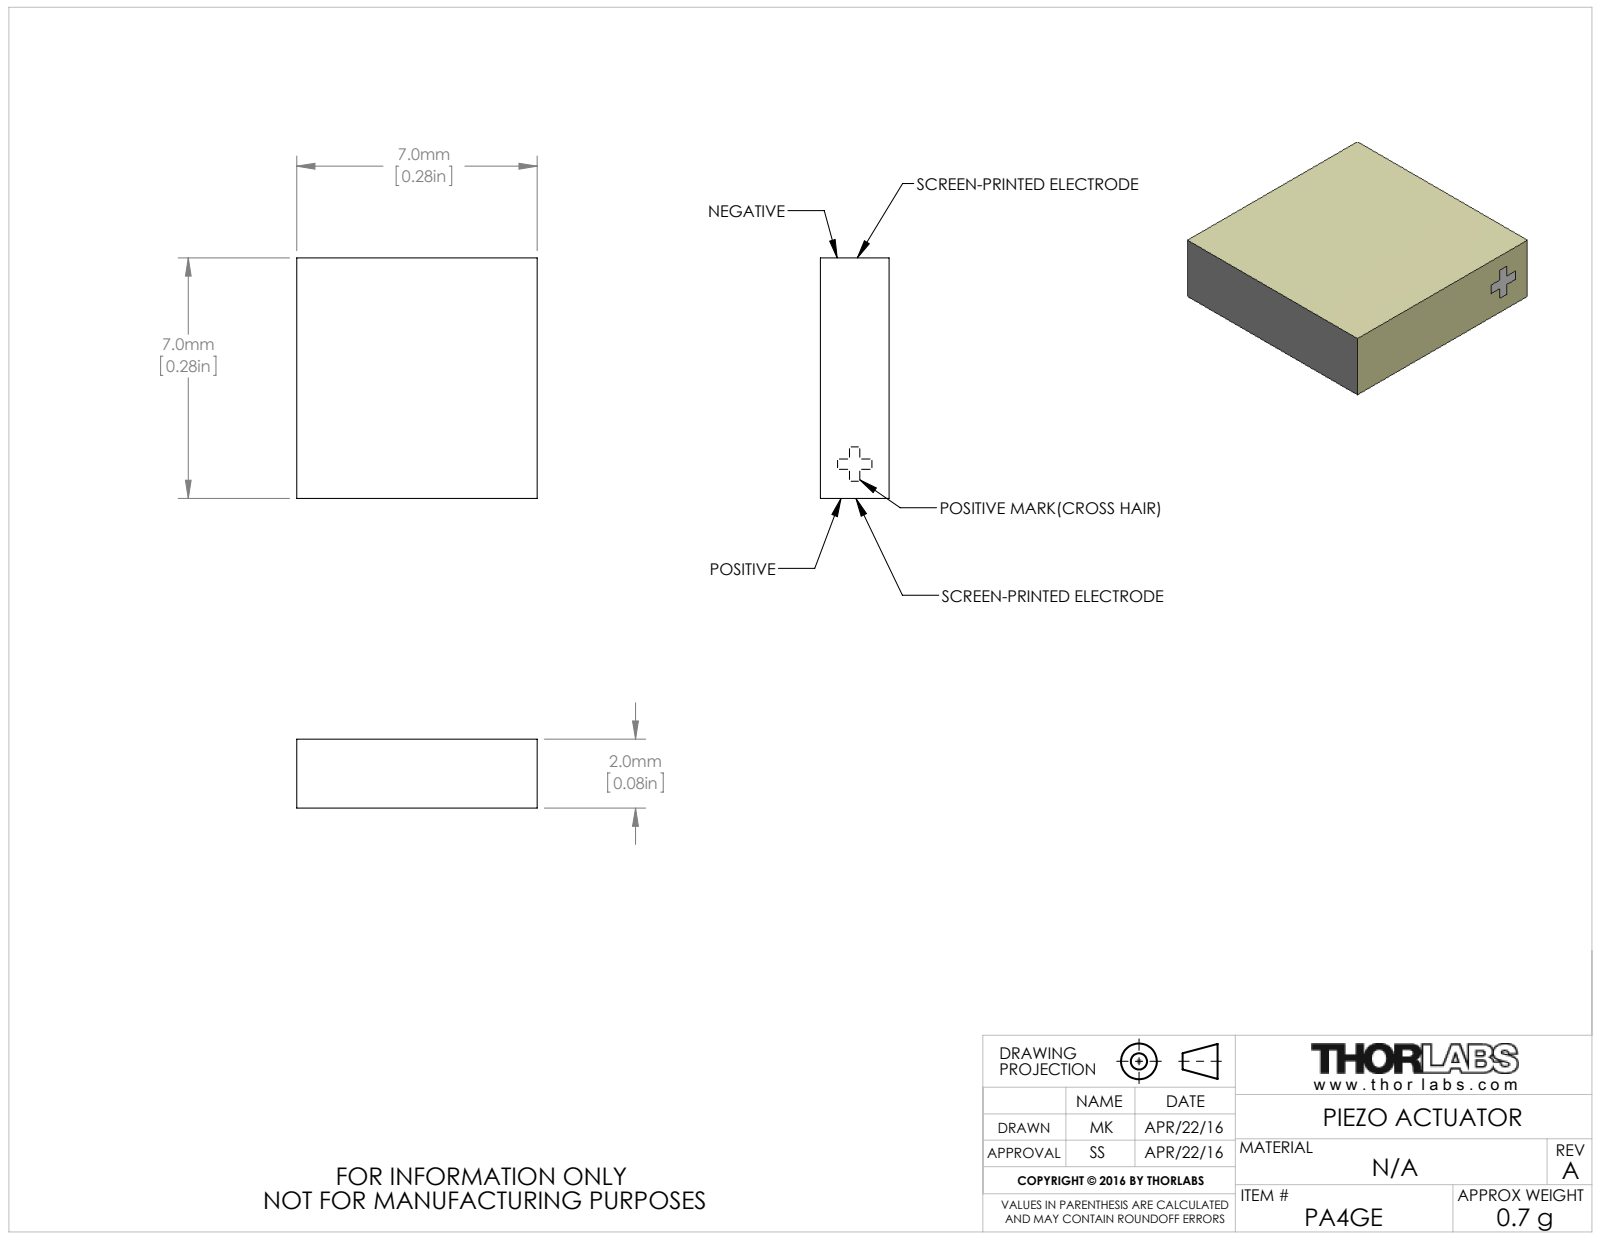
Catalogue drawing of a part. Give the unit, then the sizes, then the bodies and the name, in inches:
Units: inches
Overall size (bounding box): 0.276 × 0.276 × 0.079
Main face-to-face distances: 0.079, 0.276
Volume: 0.006 in³ · Surface area: 0.239 in²
Bodies: 1 solid, 7 faces (7 planar, 0 cylindrical, 0 other)
Part name (STEP PRODUCT): CTN002589
STEP written by: SolidWorks 2014 (AUTOMOTIVE_DESIGN)
